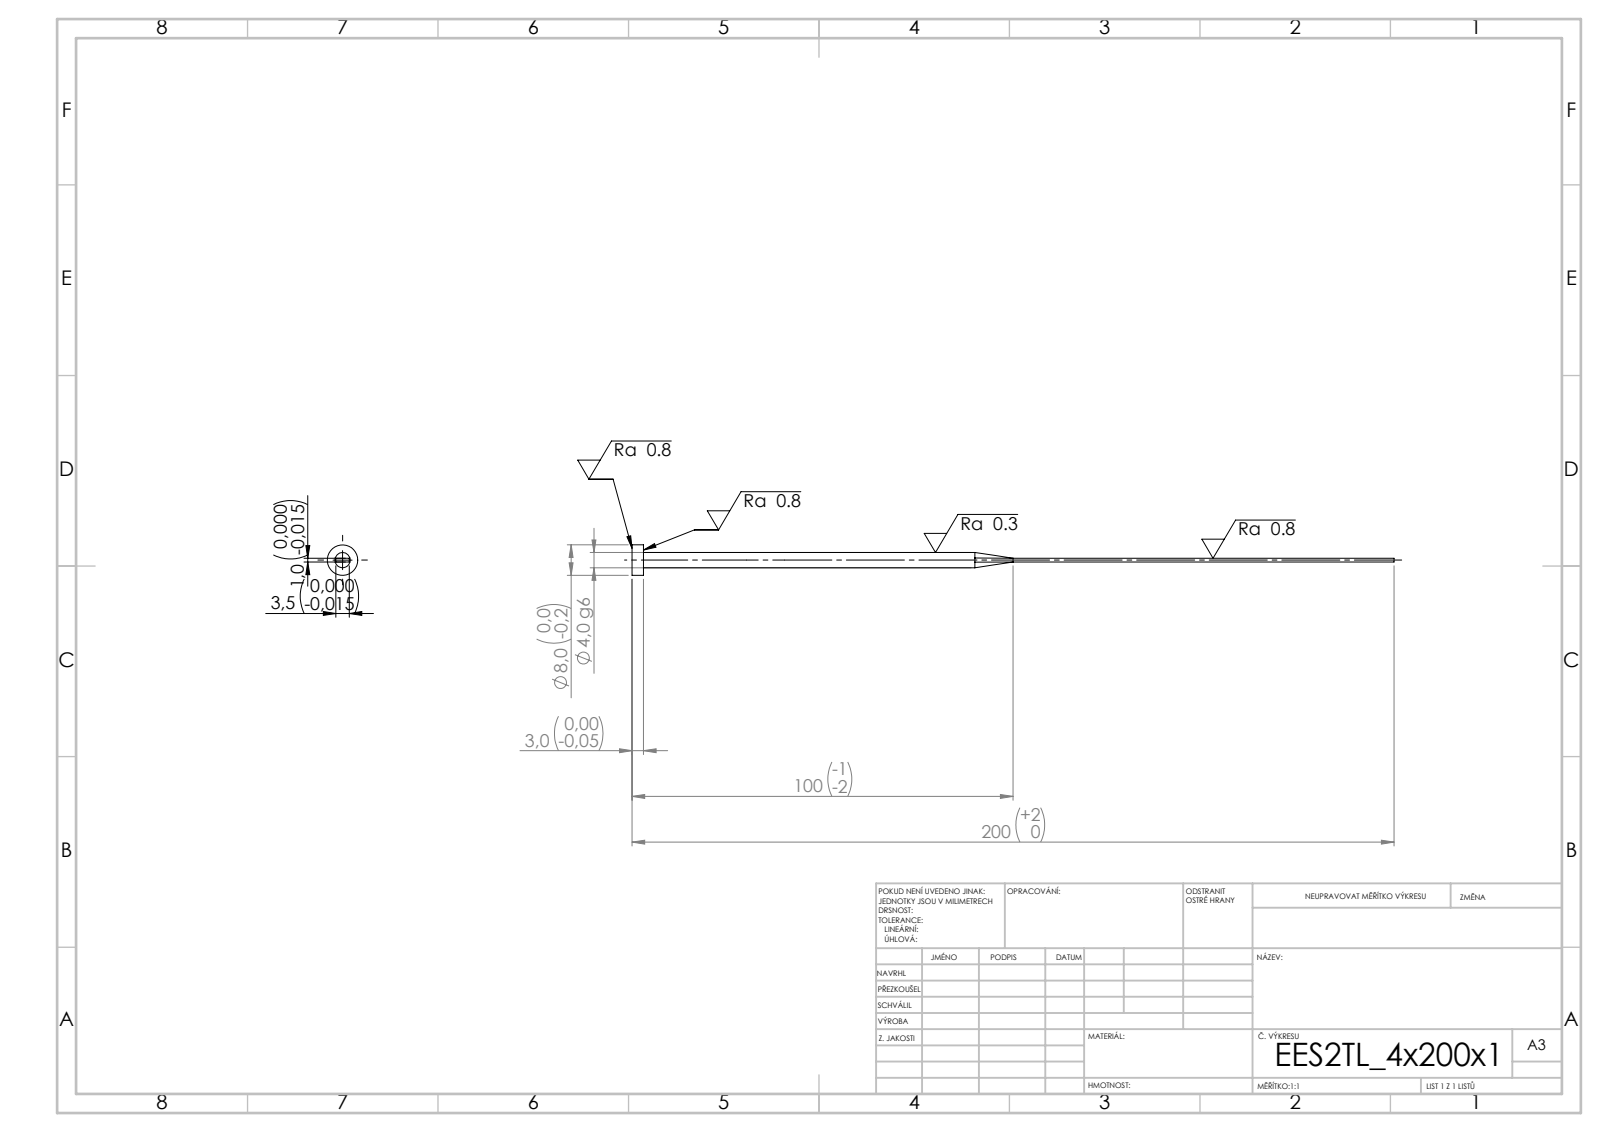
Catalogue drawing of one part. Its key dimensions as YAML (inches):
step_written_by: "SolidWorks 2019 (CONFIG_CONTROL_DESIGN)"
units: inches
bodies: {solids: 1, faces: 15, planar: 7, cylindrical: 4, other: 4}
overall_size: [7.874, 0.315, 0.315]
volume: 0.102
surface_area: 3.509
round_bosses_or_shafts:
  - {diameter: 0.315, count: 1}
  - {diameter: 0.157, count: 1}
face_to_face_distances: [0.039, 0.138, 0.118, 7.874, 7.756]
